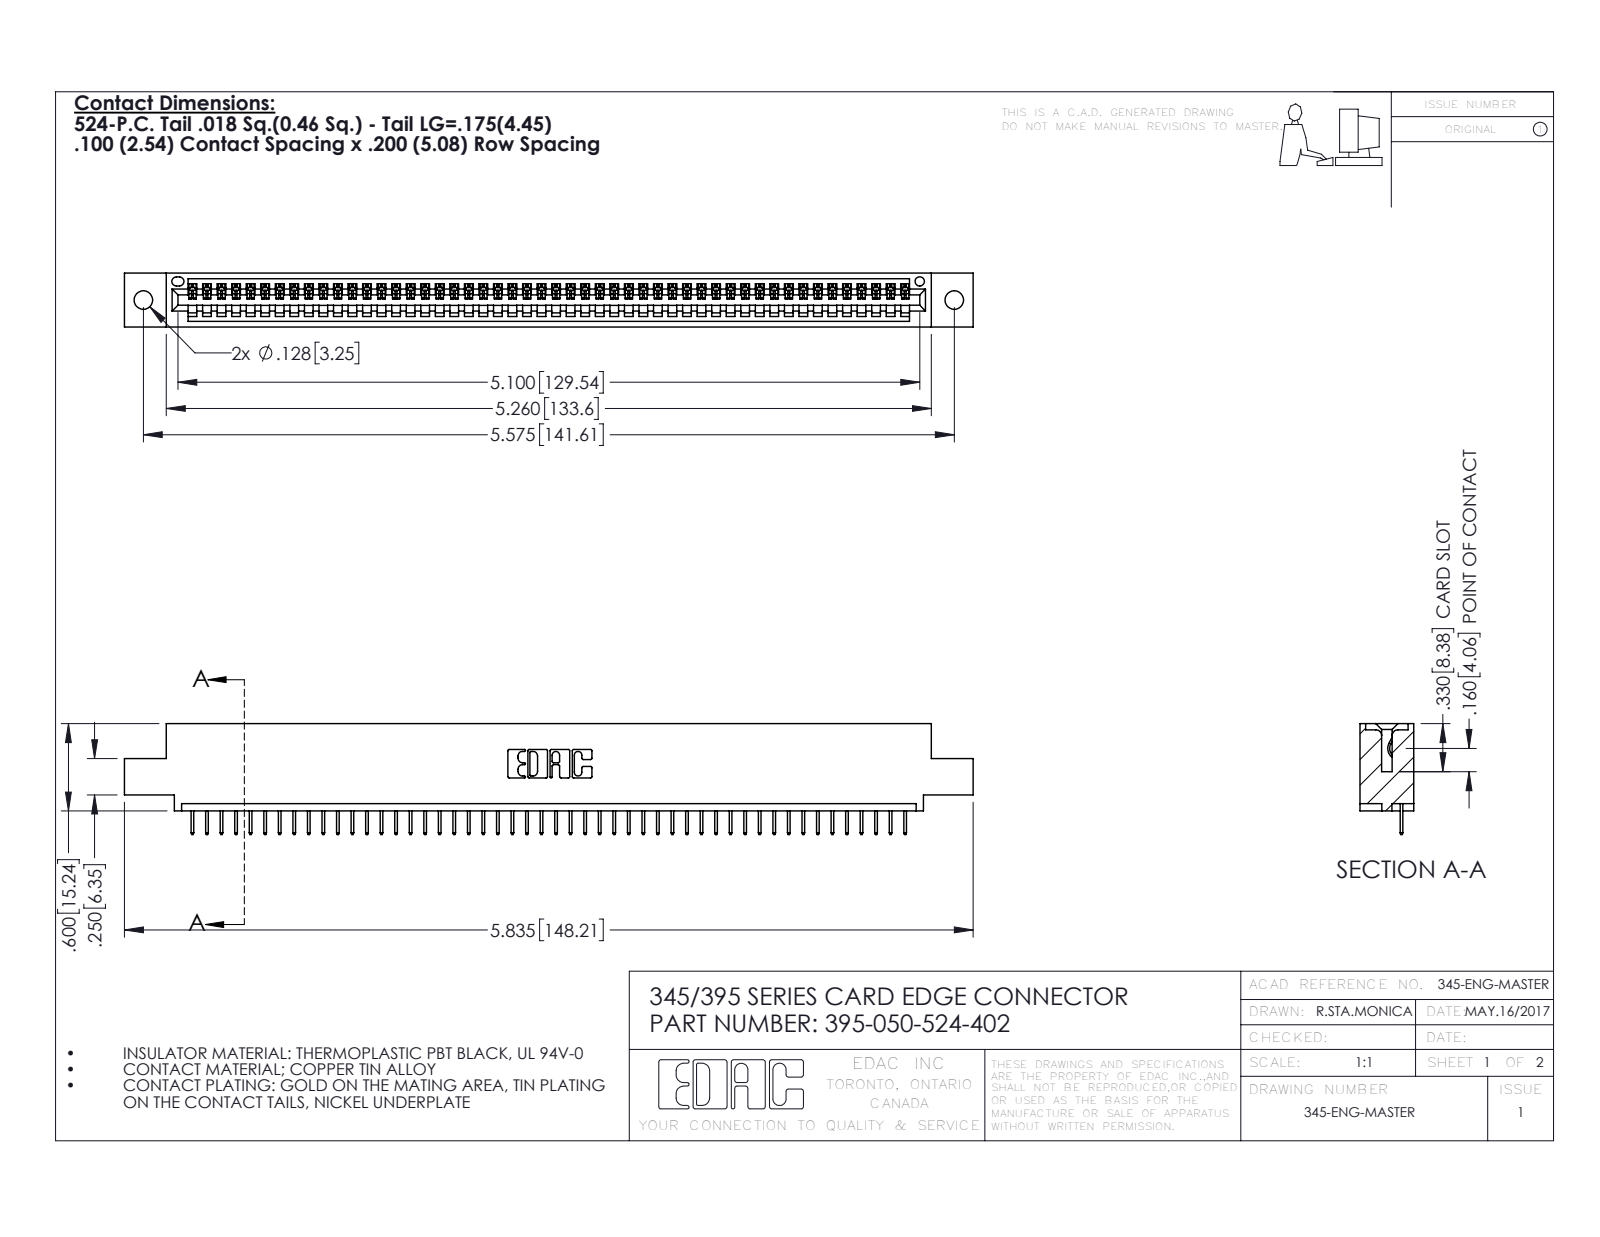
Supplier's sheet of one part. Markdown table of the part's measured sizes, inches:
| quantity | value |
| --- | --- |
| part name | 345 Part_0.110 Offset - 0.128 Dia; 395-050-524-402; 345-292-001_345-293-124 |
| STEP written by | SolidWorks 2016 (CONFIG_CONTROL_DESIGN) |
| units | inches |
| bodies | 51 solids, 3230 faces (2384 planar, 846 cylindrical, 0 other) |
| overall size | 5.835 × 0.762 × 0.37 |
| volume | 0.844 in³ |
| surface area | 27.39 in² |
| round holes (diameter × count) | 0.128 × 2, 0.064 × 1 |
| partial cylindrical surfaces (radius × count) | 0.006 × 100, 0.01 × 22, 0.007 × 6, 0.031 × 6, 0.026 × 3, 0.031 × 2, 0.04 × 2, 0.014 × 1 |
| main face-to-face distances | 0.072, 0.298, 0.37, 0.2, 0.098, 0.272, 0.025, 0.225, 0.072, 0.149 |
| hole center spacings | 0.27, 5.339, 5.575 |
